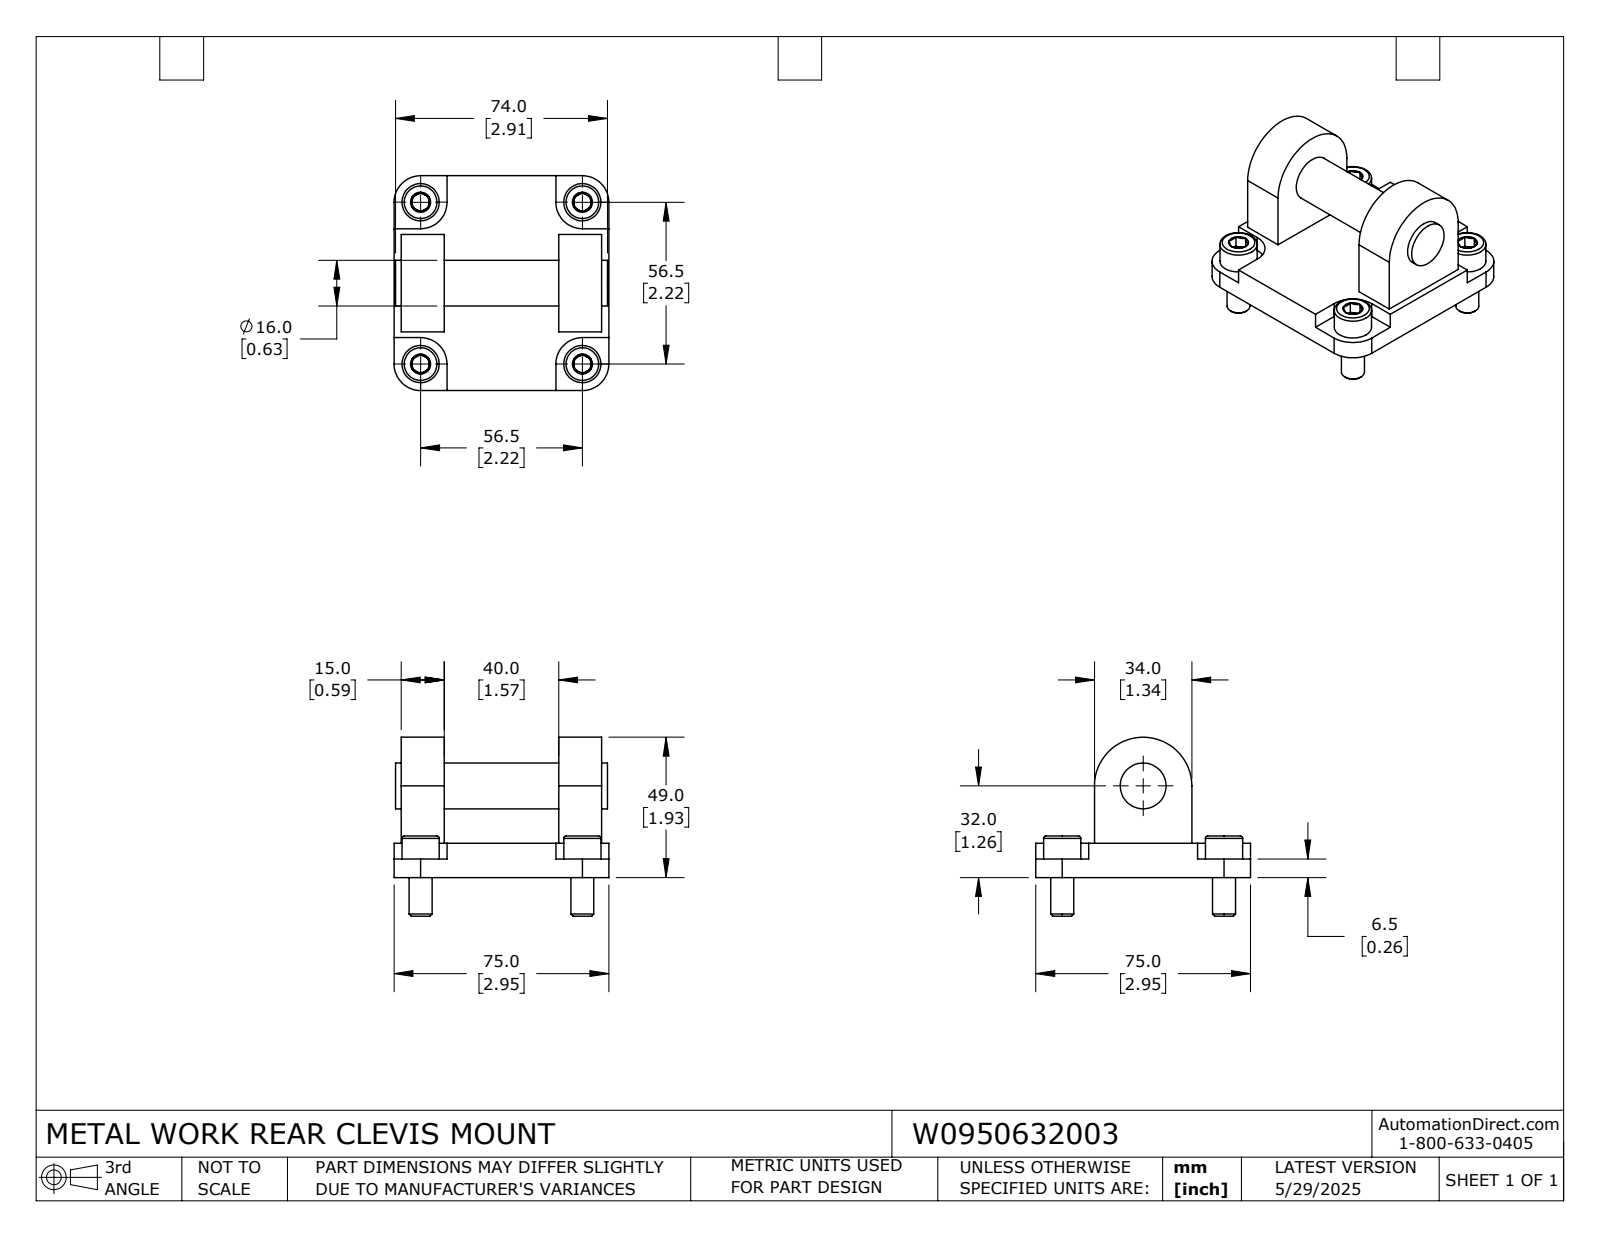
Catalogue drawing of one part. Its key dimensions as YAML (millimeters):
part_name: "W0950632003"
step_written_by: "SolidWorks 2024 (CONFIG_CONTROL_DESIGN)"
units: millimeters
bodies: {solids: 5, faces: 187, planar: 89, cylindrical: 42, other: 56}
overall_size: [75, 75, 62.5]
volume: 97650
surface_area: 28440
round_holes:
  - {diameter: 9, count: 4}
  - {diameter: 45, count: 1}
round_bosses_or_shafts:
  - {diameter: 13, count: 4}
  - {diameter: 8, count: 4}
  - {diameter: 16, count: 1}
partial_cylinders:
  - {radius: 9.2, count: 4}
  - {radius: 17, count: 1}
face_to_face_distances: [12, 15, 55, 0.5, 7, 5, 2.5, 20.5, 6.5, 5.5]
hole_center_spacings: [40, 56.5, 79.9]
